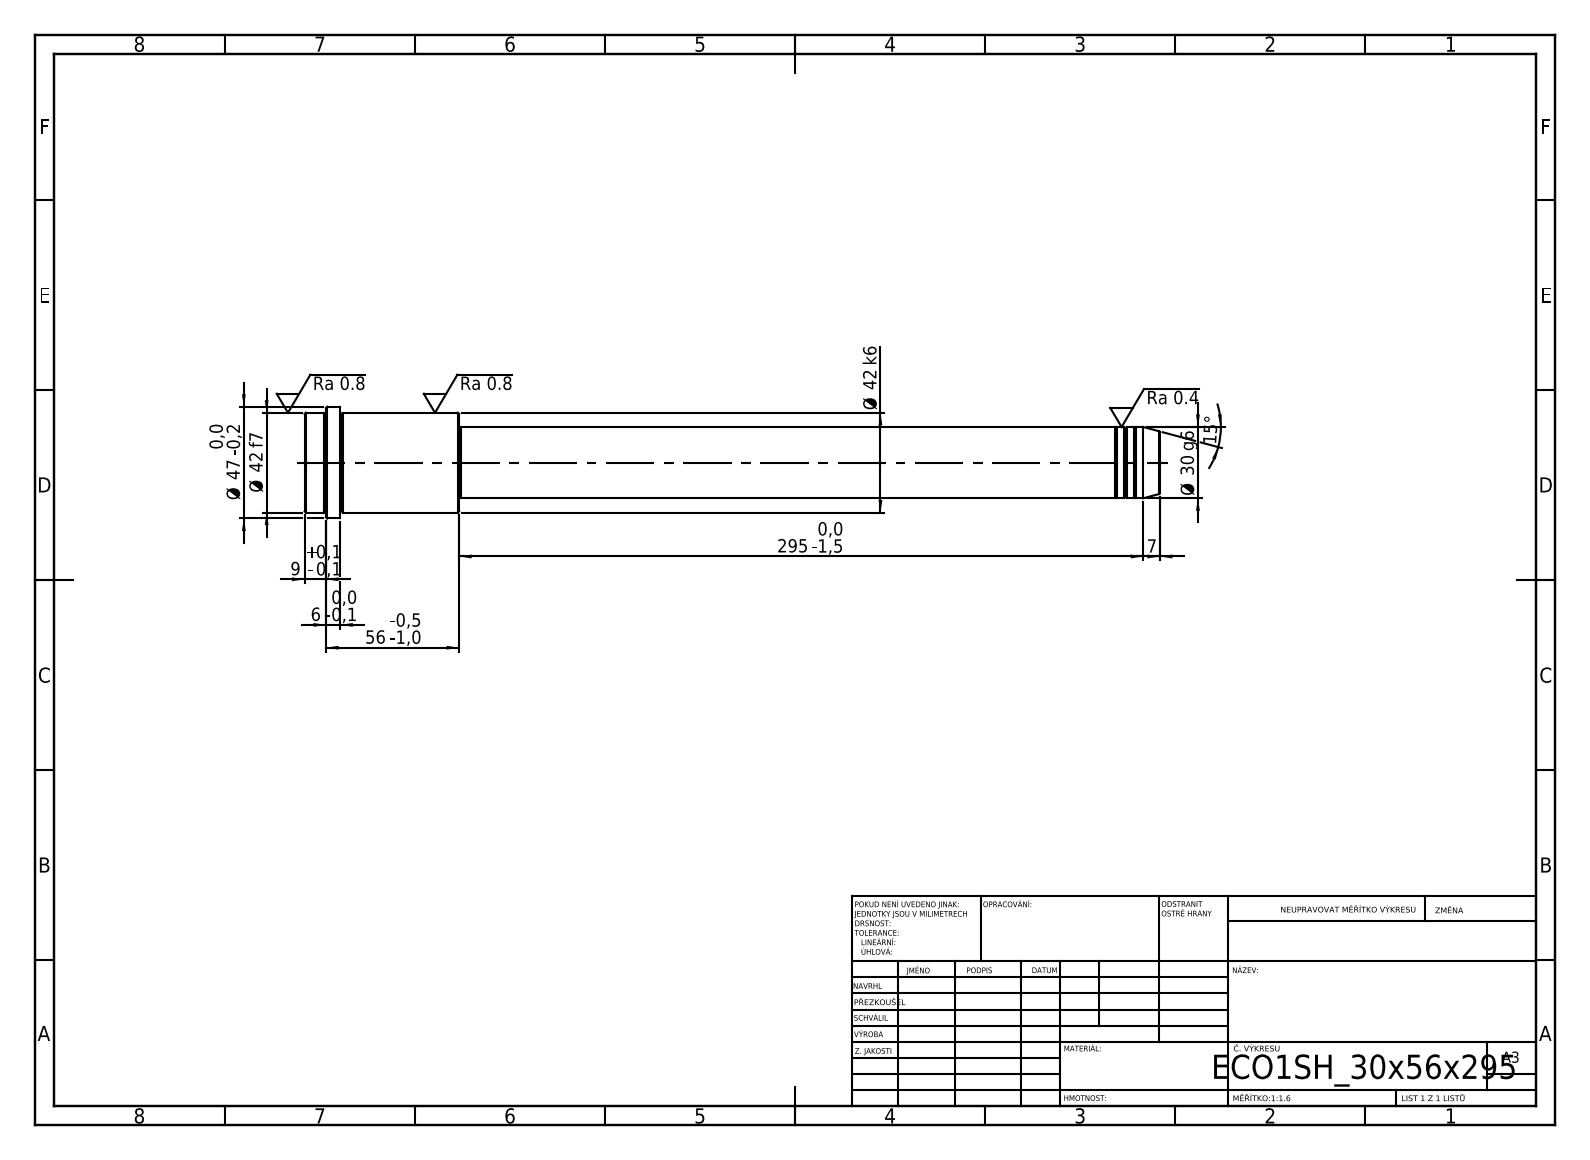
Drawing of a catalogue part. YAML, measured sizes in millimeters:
step_written_by: "SolidWorks 2019 (CONFIG_CONTROL_DESIGN)"
units: millimeters
bodies: {solids: 1, faces: 52, planar: 6, cylindrical: 16, other: 30}
overall_size: [360, 47, 47]
volume: 299769
surface_area: 40014
round_bosses_or_shafts:
  - {diameter: 47, count: 1}
  - {diameter: 42, count: 1}
  - {diameter: 30, count: 1}
  - {diameter: 29, count: 1}
face_to_face_distances: [65, 295, 360, 345, 50, 15, 351, 56, 6, 9]
